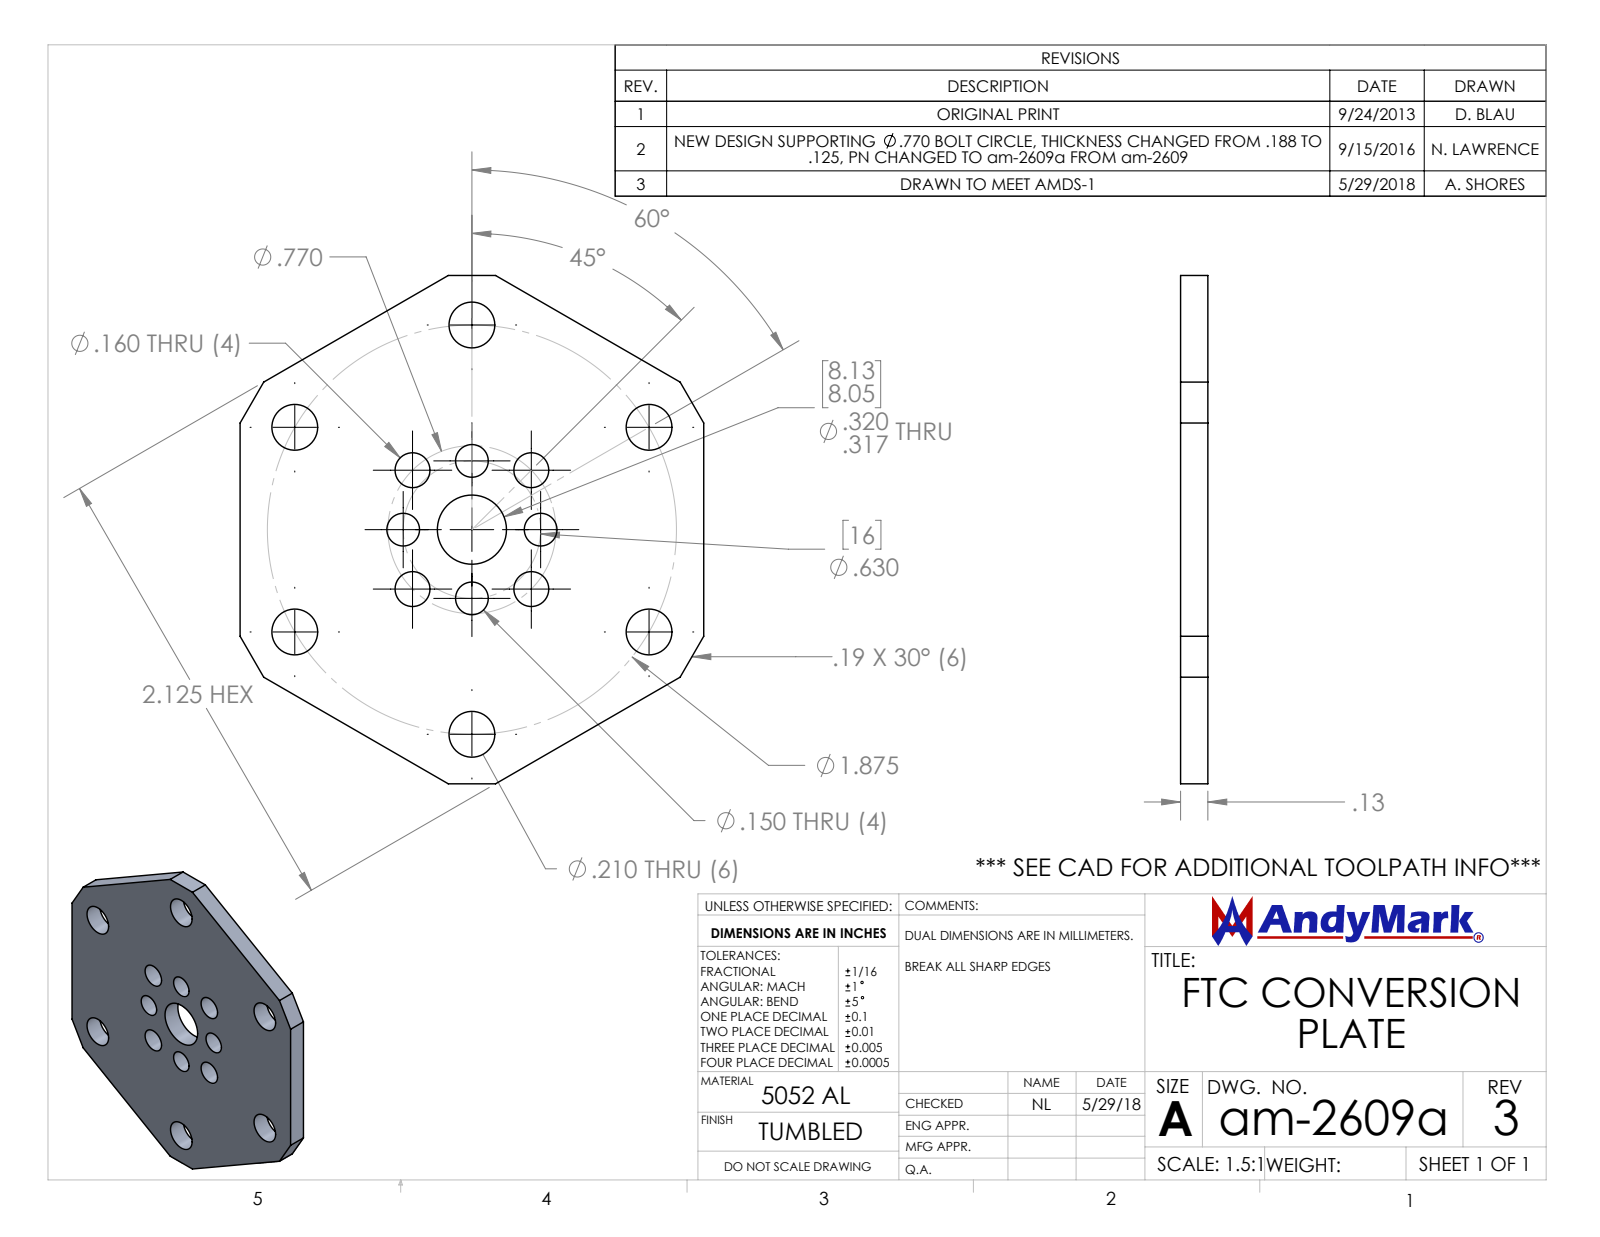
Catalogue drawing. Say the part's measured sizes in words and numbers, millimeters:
The part is named "am-2609a FTC Conversion Plate REV 3". Its 3-D file was written by "SolidWorks 2019 (AUTOMOTIVE_DESIGN)". It is 1 solid with 29 faces: 14 planar, 15 cylindrical and 0 other. Overall it measures 59.2 by 54 by 3.2 millimeters. Its volume is 7 030 cubic millimeters and its surface area 5 720 square millimeters. Round holes: 6 of diameter 5.3, 4 of diameter 3.8, 4 of diameter 4.1, 1 of diameter 8.1. The main face-to-face distances are 3.2, 54, 59.1. The hole center spacings are 23.8, 7, 16.4, 41.2, 8, 9.8, 11.3, 13.8.
